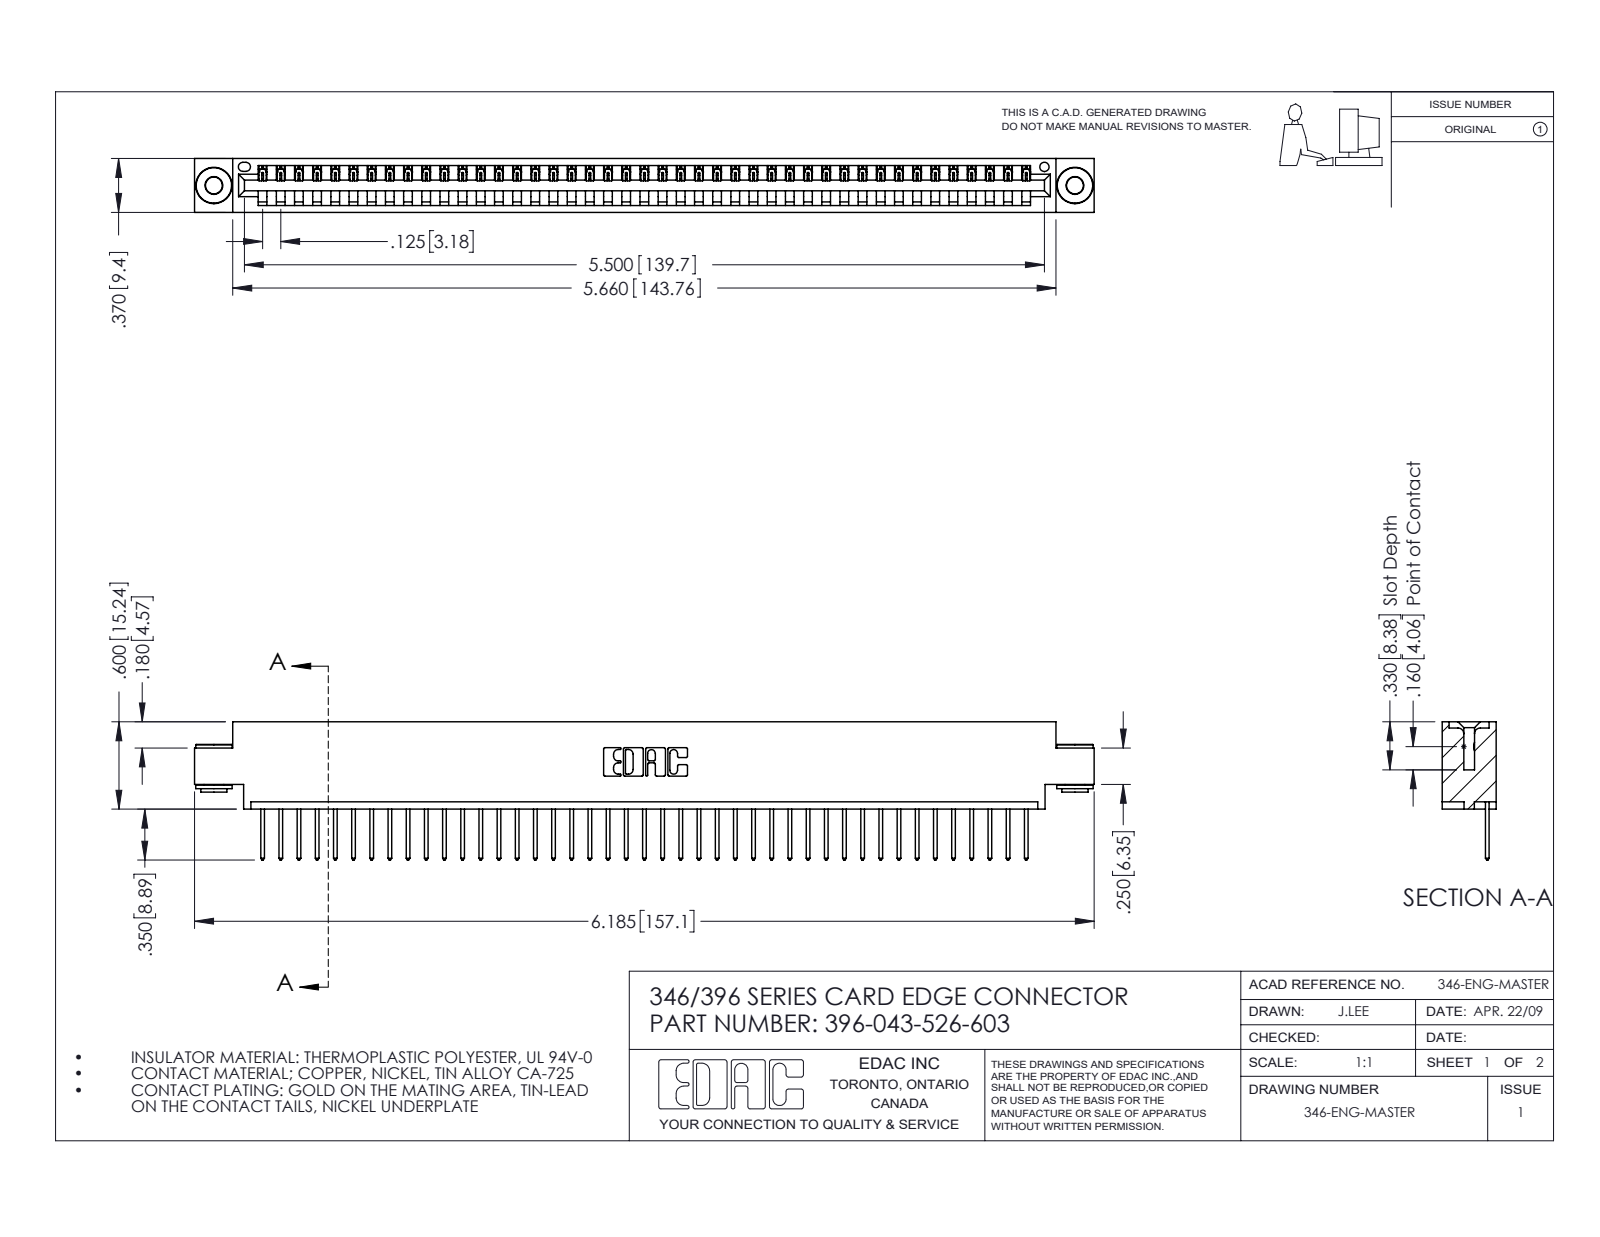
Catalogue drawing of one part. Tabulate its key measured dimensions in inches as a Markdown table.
| quantity | value |
| --- | --- |
| part name | 396-043-526-603; 345-292-001_345-293-126; 345-250-002_345-250-002-102; 346 Part_0.170 Offset - 0.156 Dia-TH |
| STEP written by | SolidWorks 2016 (CONFIG_CONTROL_DESIGN) |
| units | inches |
| bodies | 46 solids, 2658 faces (1810 planar, 840 cylindrical, 8 other) |
| overall size | 6.185 × 0.95 × 0.37 |
| volume | 0.908 in³ |
| surface area | 29.36 in² |
| round holes (diameter × count) | 0.116 × 2, 0.156 × 2, 0.064 × 1 |
| round bosses / shafts (diameter × count) | 0.25 × 2, 0.18 × 2, 0.136 × 2 |
| partial cylindrical surfaces (radius × count) | 0.006 × 86, 0.01 × 86, 0.01 × 22, 0.007 × 6, 0.031 × 6, 0.026 × 3, 0.031 × 2, 0.04 × 2 |
| main face-to-face distances | 0.048, 0.322, 0.37, 0.25, 0.025, 0.072, 0.298, 0.148, 0.222, 0.1 |
| hole center spacings | 0.246, 5.711, 5.92 |
